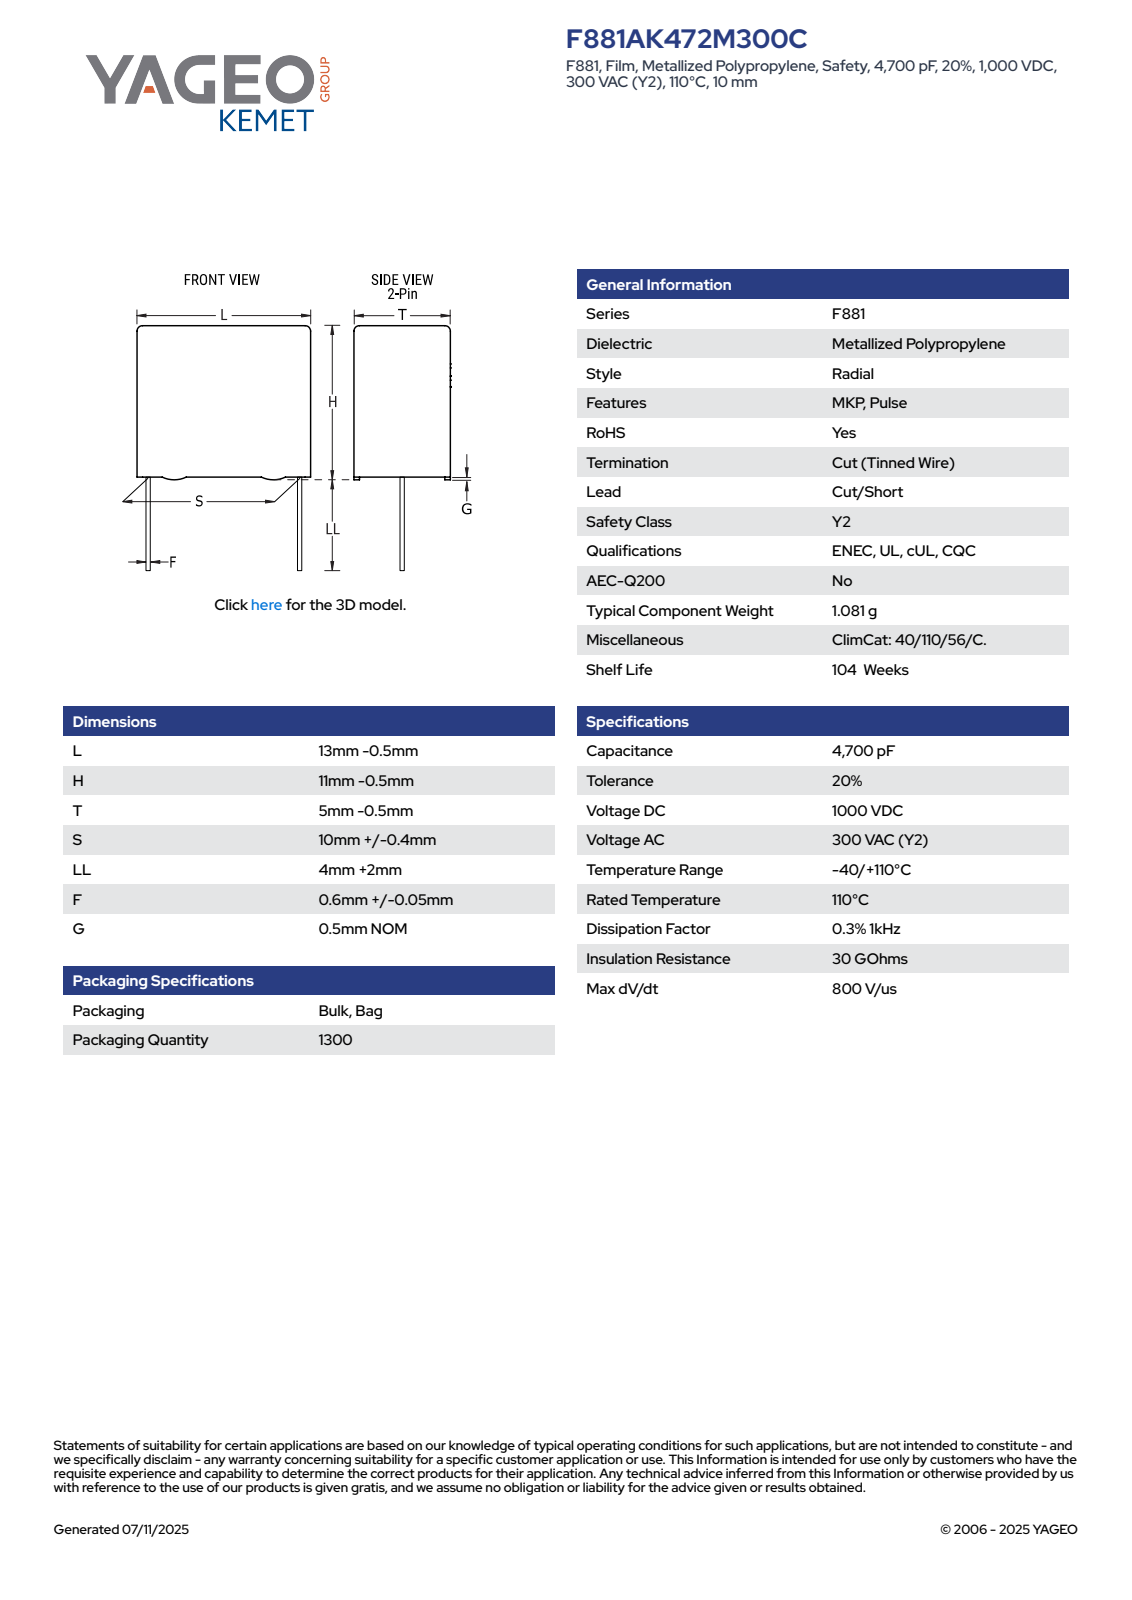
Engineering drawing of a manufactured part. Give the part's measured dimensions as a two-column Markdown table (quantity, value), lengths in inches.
| quantity | value |
| --- | --- |
| part name | CFR_RBG_13X11X5_L12.5H10.5T4.5S10LL6F0.65G0.5 |
| STEP written by | SolidWorks 2014 (AUTOMOTIVE_DESIGN) |
| units | inches |
| bodies | 4 solids, 89 faces (81 planar, 8 cylindrical, 0 other) |
| overall size | 0.65 × 0.492 × 0.177 |
| volume | 0.035 in³ |
| surface area | 0.772 in² |
| round bosses / shafts (diameter × count) | 0.026 × 2 |
| partial cylindrical surfaces (radius × count) | 0.02 × 4 |
| main face-to-face distances | 0.177, 0.492, 0.394, 0.167, 0.157, 0.02, 0.413, 0.236, 0.256, 0.65 |
